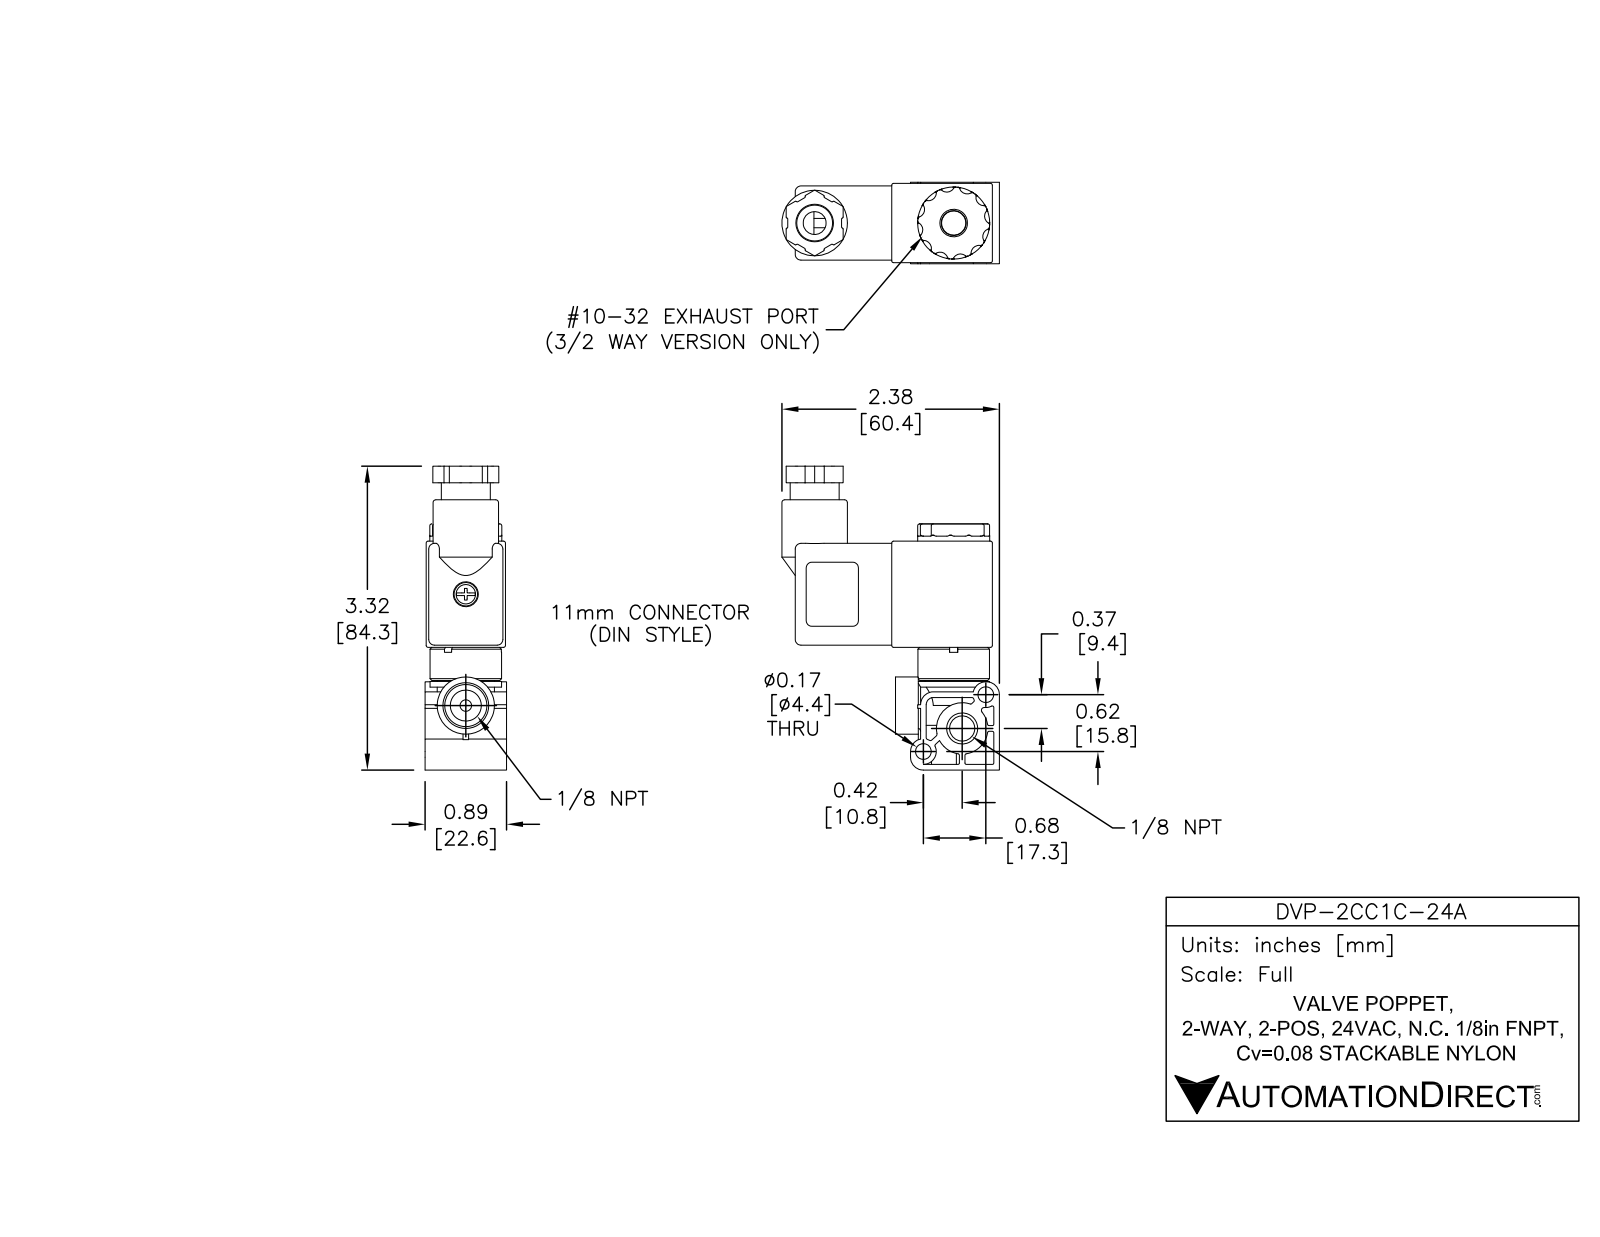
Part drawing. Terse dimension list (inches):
name: DVP-2CC1C-24A
written by: SolidWorks 2015 (AUTOMOTIVE_DESIGN)
unit: in
bodies: 2 solids, 1445 faces (660 planar, 308 cylindrical, 477 other)
size: 3.32 × 2.377 × 0.89
volume: 2.136 in³; area: 39.16 in²
holes: 2× ⌀0.1, 2× ⌀0.125, 2× ⌀0.15, 2× ⌀0.172, 2× ⌀0.339, 1× ⌀0.102, 1× ⌀0.166, 1× ⌀0.25, 1× ⌀0.268, 1× ⌀0.272, 1× ⌀0.275, 1× ⌀0.321
bosses: 2× ⌀0.625, 1× ⌀0.787, 1× ⌀0.781, 1× ⌀0.716, 1× ⌀0.538, 1× ⌀0.536, 1× ⌀0.522, 1× ⌀0.5
rounds: 28× R0.015, 25× R0.01, 24× R0.025, 12× R0.02, 12× R0.062, 12× R0.088, 5× R0.031, 4× R0.141
face distances: 0.078, 0.788, 0.05, 0.8, 0.76, 0.028, 0.838, 0.866, 1.136, 0.71
hole spacings: 0.327, 0.42, 0.45, 0.493, 0.522, 0.731, 0.922, 0.944
